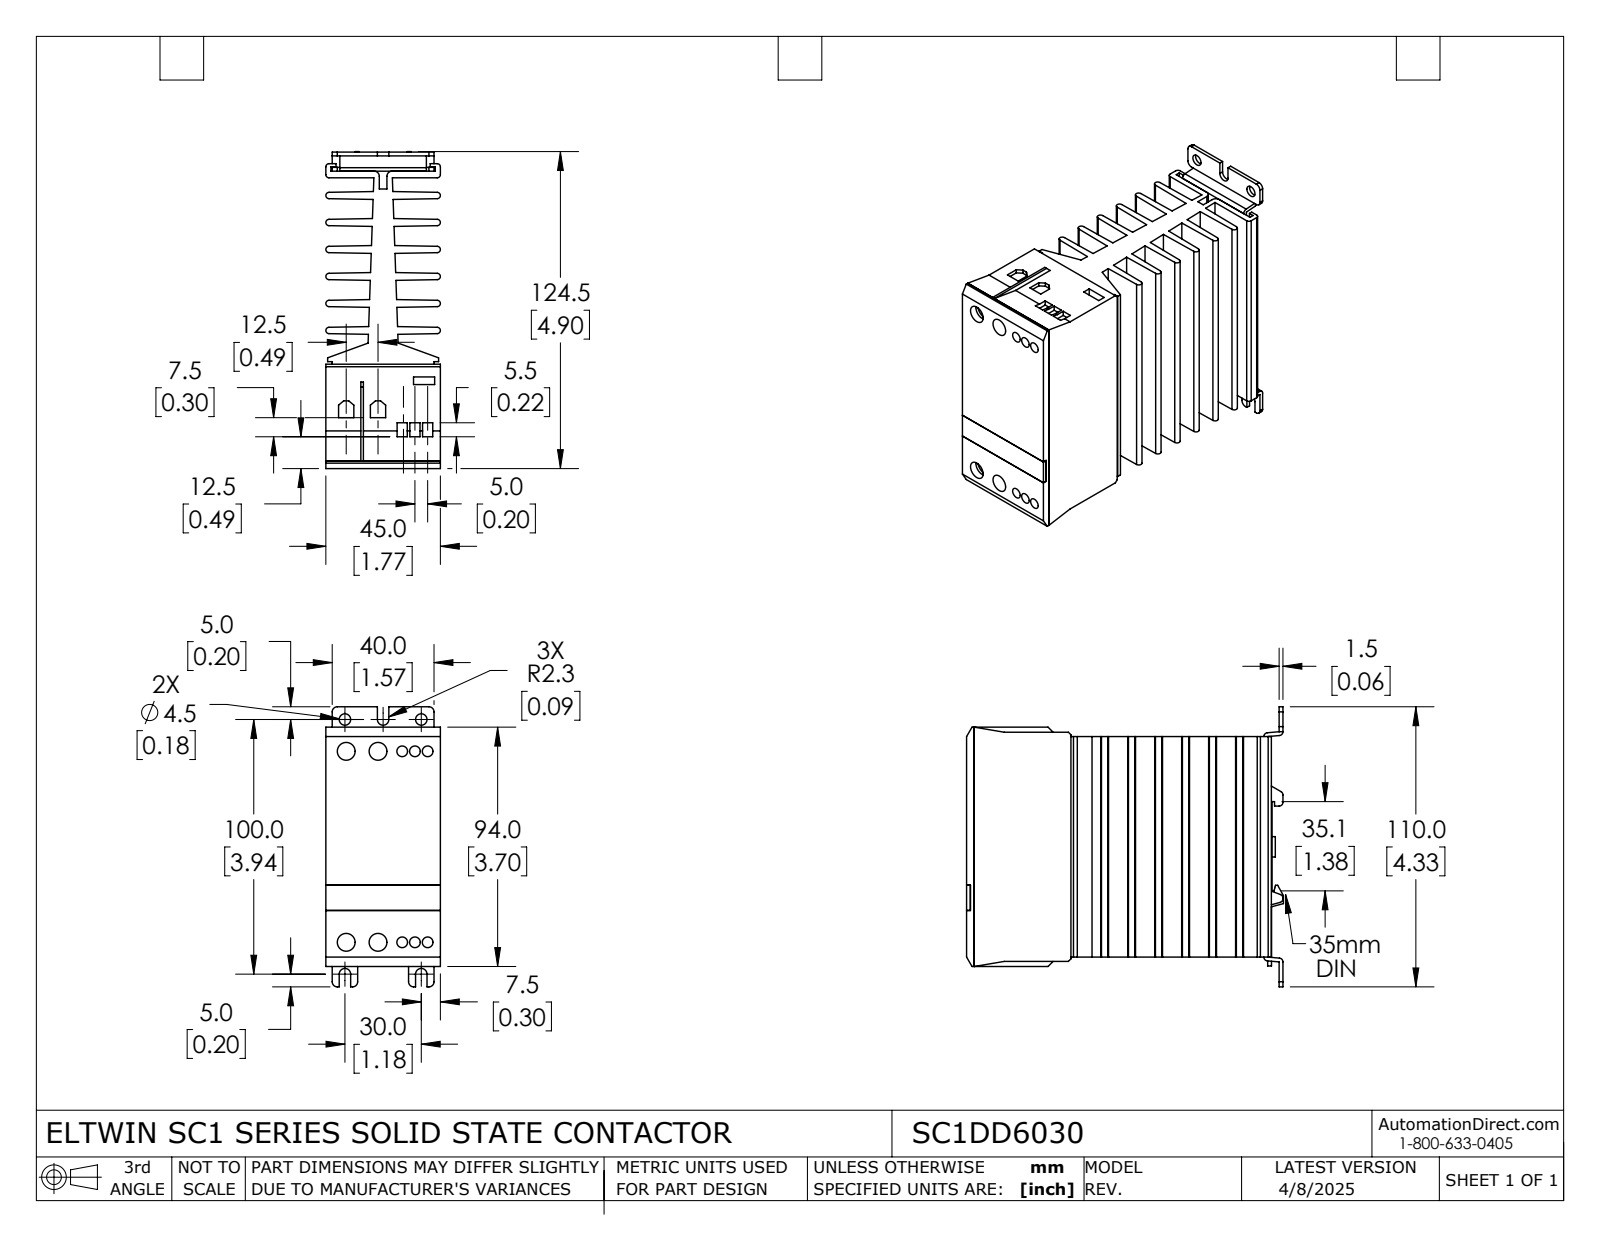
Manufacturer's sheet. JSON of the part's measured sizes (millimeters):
{"part_name": "SC1DD6030", "step_written_by": "SolidWorks 2021 (AUTOMOTIVE_DESIGN)", "units": "millimeters", "bodies": {"solids": 7, "faces": 391, "planar": 284, "cylindrical": 107, "other": 0}, "overall_size": [124.5, 110, 45], "volume_mm3": 309200, "surface_area_mm2": 106700, "round_holes": [[4.2, 6], [4.4, 6], [7, 4], [4.5, 2], [8, 2]], "round_bosses_or_shafts": [[8, 3]], "partial_cylinders_radius": [[2, 18], [1.2, 16], [1.5, 10], [1.3, 4], [2.3, 3]], "face_to_face_distances": [10.6, 21.2, 3.2, 31.8, 7.4, 13.8, 18, 24.4, 42.4, 28.6], "hole_center_spacings": [75, 5, 75.2, 9.5, 10, 12.5, 12.8, 14.5]}
